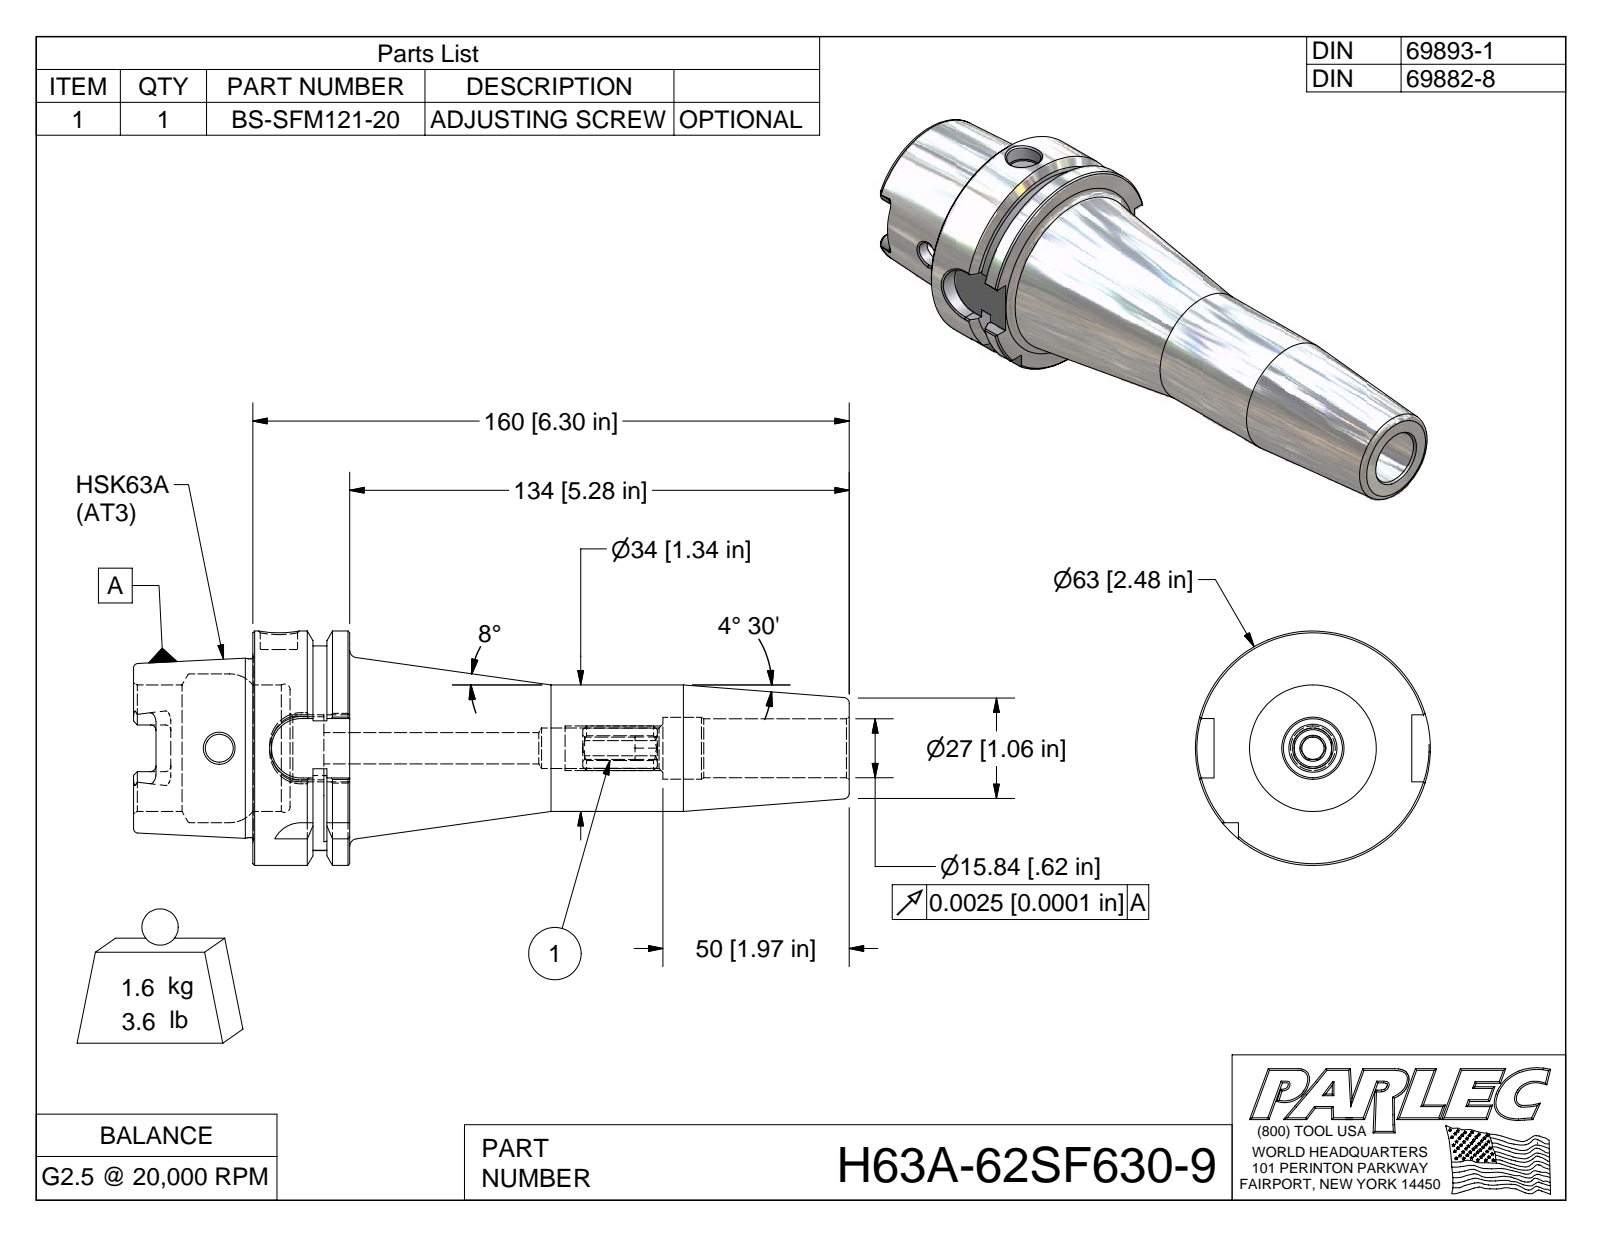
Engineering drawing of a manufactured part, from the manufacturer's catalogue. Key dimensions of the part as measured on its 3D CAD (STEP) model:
Part name (STEP PRODUCT): H63A-62SF630-9; H63A-62SF630-9-1; BS-SFM121-20
STEP written by: Autodesk Inventor 2009 (AUTOMOTIVE_DESIGN)
Units: inches
Bodies: 2 solids, 160 faces (59 planar, 35 cylindrical, 66 other)
Overall size (bounding box): 7.559 × 2.48 × 2.48
Volume: 12.59 in³ · Surface area: 65.45 in²
Round holes (diameter × count): ⌀0.295 ×1, ⌀0.394 ×1, ⌀0.624 ×1, ⌀0.654 ×1, ⌀0.666 ×1, ⌀1.339 ×1, ⌀1.575 ×1
Round bosses / shafts (diameter × count): ⌀2.48 ×1, ⌀1.891 ×1
Partial cylindrical surfaces — rounded edges, fillets, slot ends (radius × count): R0.059 ×6, R0.113 ×4, R0.315 ×4, R0.236 ×1, R1.083 ×1
Main face-to-face distances: 1.024, 0.394, 0.241, 0.389, 0.63, 1.26, 1.654, 2.283, 1.894, 0.635
